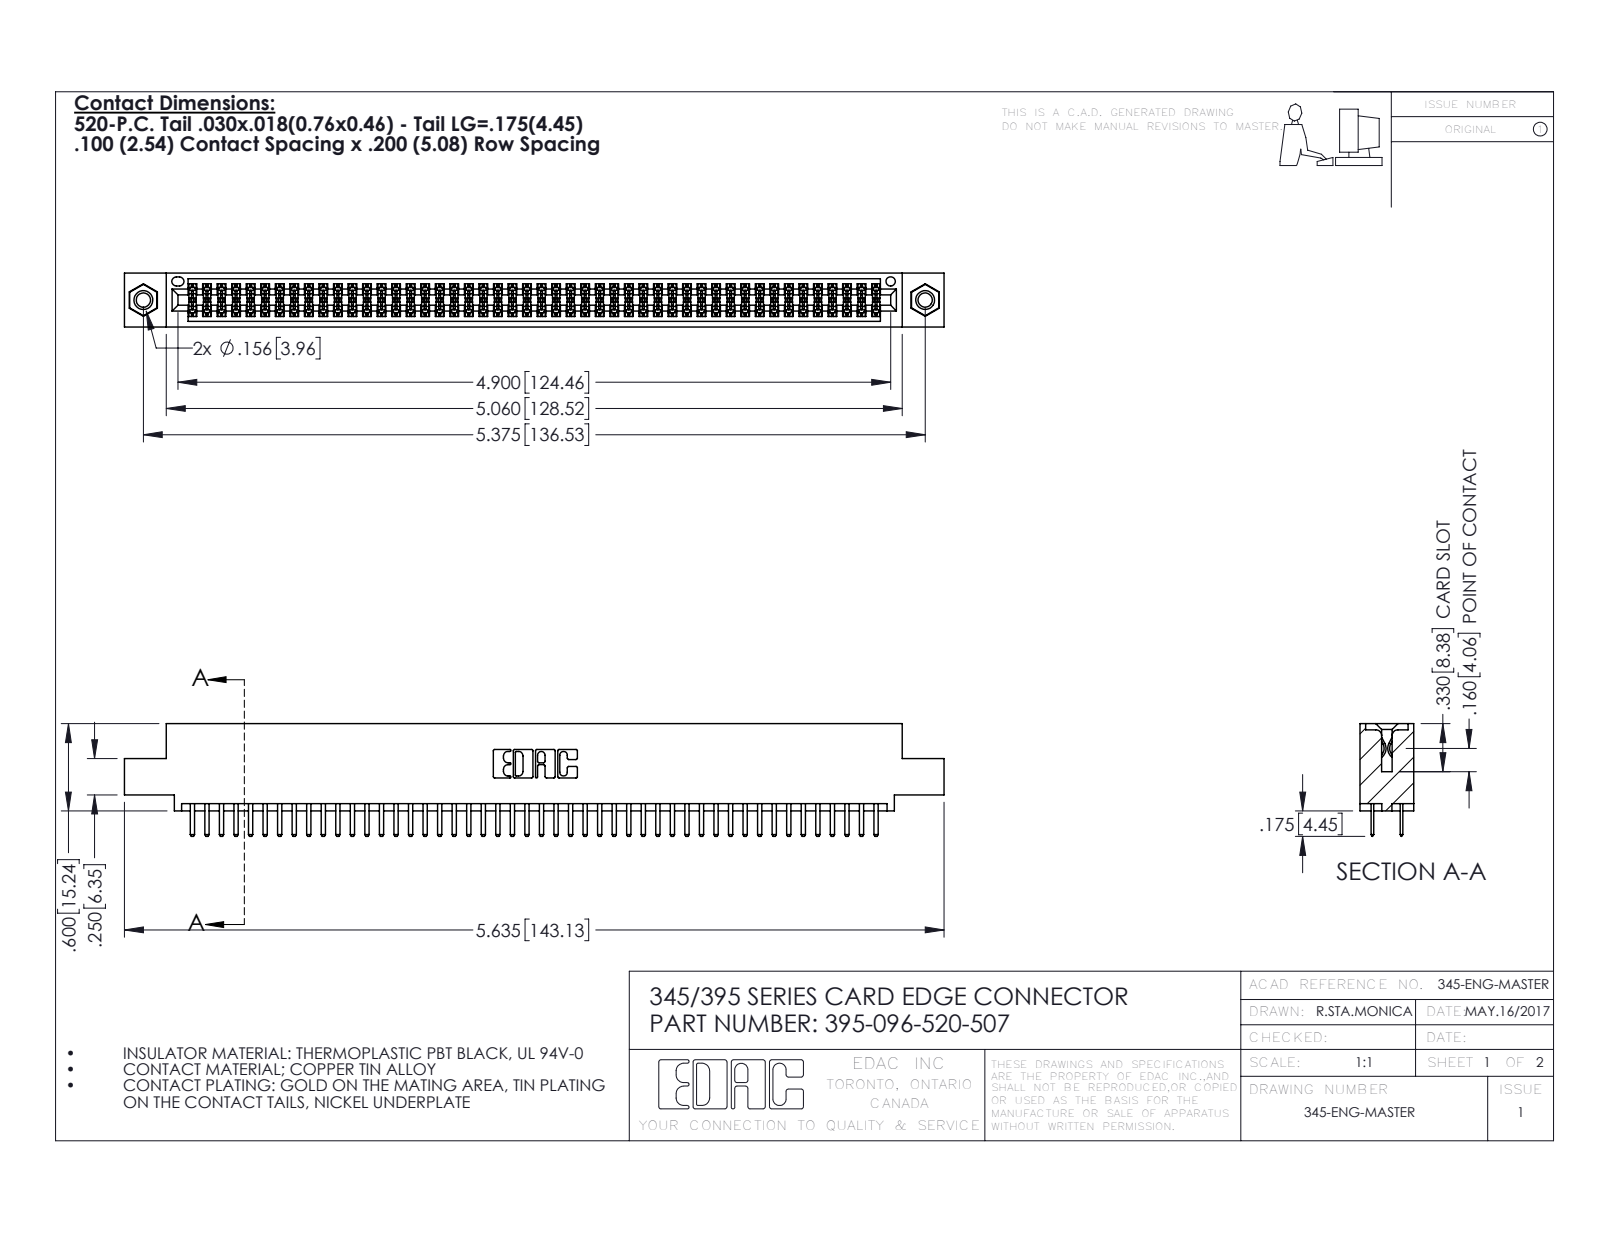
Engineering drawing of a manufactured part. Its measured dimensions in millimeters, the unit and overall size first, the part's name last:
Units: millimetres
Overall size (bounding box): 143.1 × 19.7 × 9.4
Round holes (diameter × count): ⌀2.5 ×2, ⌀3.2 ×2, ⌀4 ×2, ⌀1.6 ×1
Round bosses / shafts (diameter × count): ⌀3.9 ×2
Partial cylindrical surfaces — rounded edges, fillets, slot ends (radius × count): R0.2 ×144, R0.3 ×100, R0.3 ×22, R0.2 ×6, R0.8 ×6, R0.7 ×3, R0.4 ×2, R0.5 ×2
Main face-to-face distances: 1.8, 7.6, 5.1, 9.4, 2.5, 6.9, 0.6, 5.7, 0.6, 1.8
Hole centre spacings: 6.9, 130.5, 136.5
Volume: 13 800 mm³ · Surface area: 20 590 mm²
Bodies: 99 solids, 5374 faces (3476 planar, 1882 cylindrical, 16 other)
Part name (STEP PRODUCT): 395-096-520-507; 345-292-001_345-293-120; 345 Part_0.110 Offset - 0.156 Dia-TI; 345-250-001_345-250-005-103
STEP written by: SolidWorks 2016 (CONFIG_CONTROL_DESIGN)
